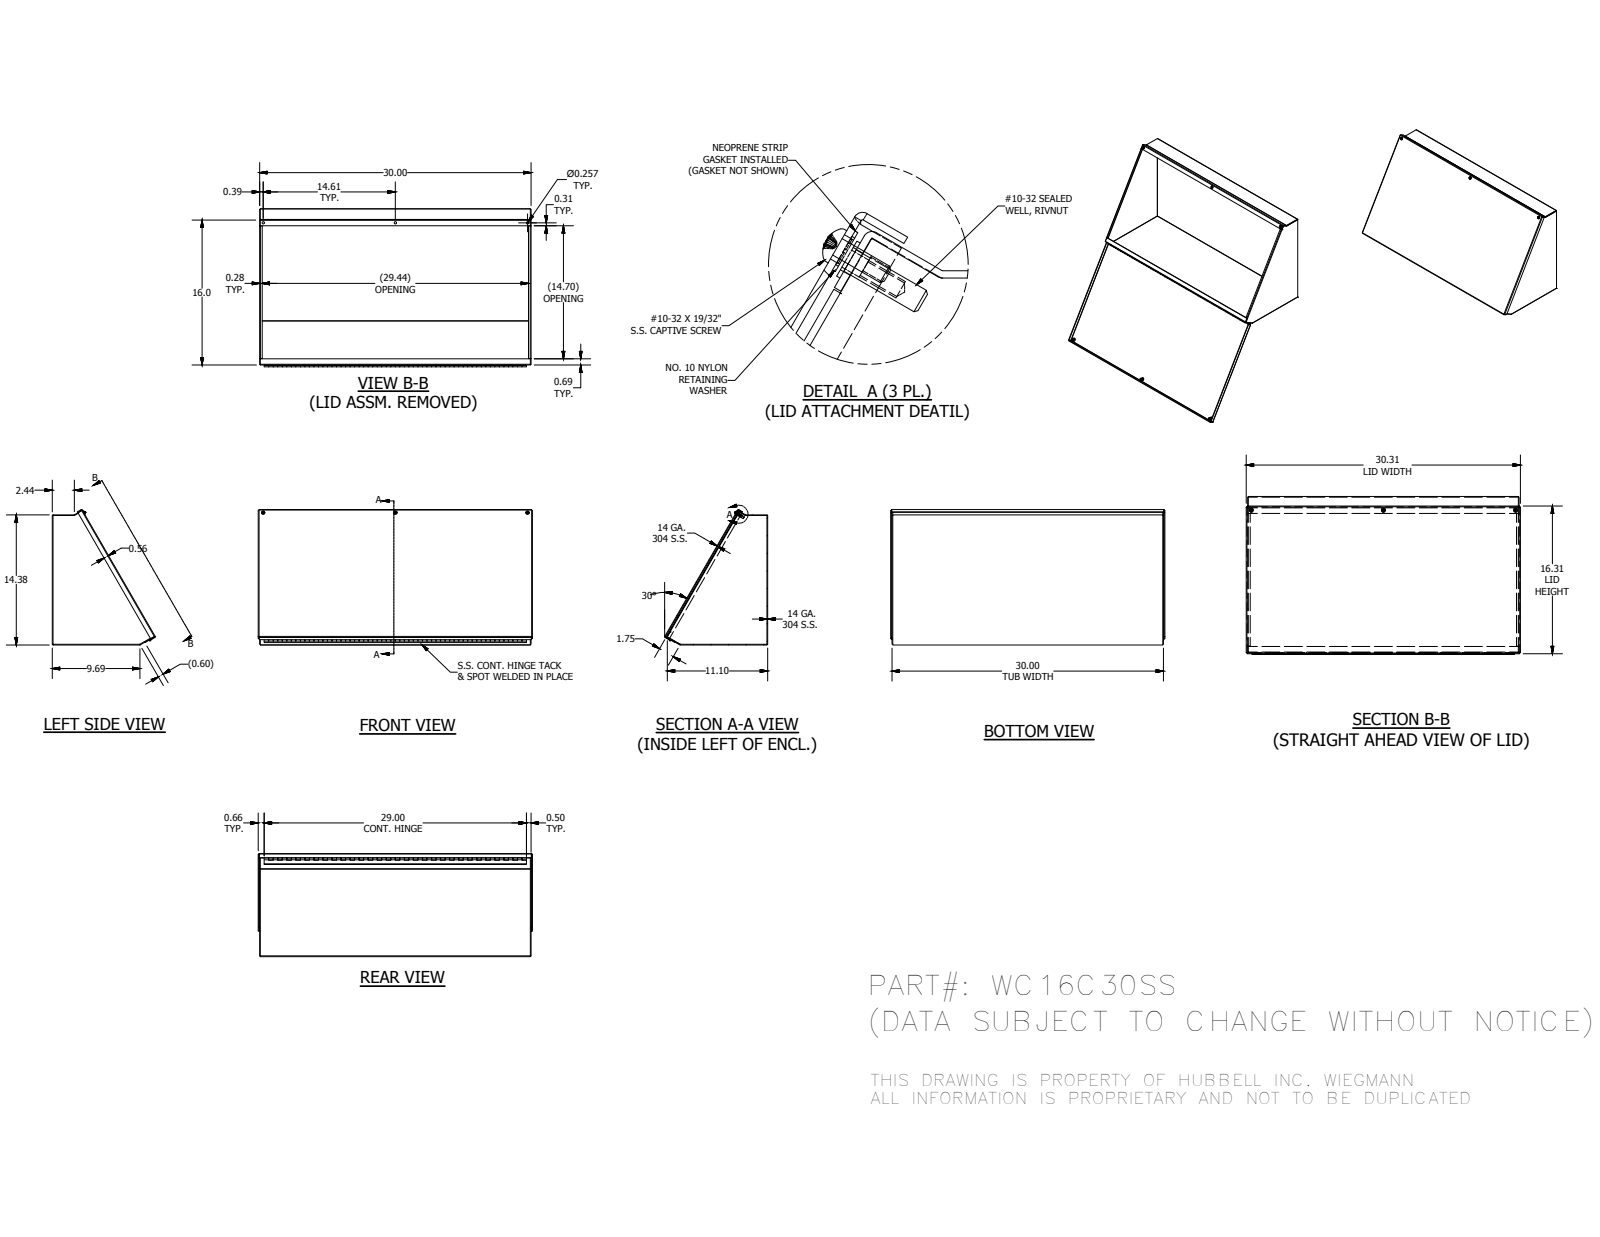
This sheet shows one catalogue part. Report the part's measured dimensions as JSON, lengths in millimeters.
{"part_name": "WC16C30SSBTB; WC16C30SSLID; WC16CSSLS; WC16CSSRS (+8 more)", "step_written_by": "Autodesk Inventor 2014 (AUTOMOTIVE_DESIGN)", "units": "millimeters", "bodies": {"solids": 16, "faces": 657, "planar": 400, "cylindrical": 183, "other": 74}, "overall_size": [769.94, 380, 289.23], "volume_mm3": 2040000, "surface_area_mm2": 2217000, "round_holes": [[3.96, 3], [4.98, 3], [6.53, 3], [7.06, 3], [7.14, 3], [2.96, 1]], "round_bosses_or_shafts": [[11.51, 3], [10.31, 3], [9.47, 3], [6.3, 3], [4.83, 3], [5.08, 1], [2.54, 1]], "partial_cylinders_radius": [[0.4, 12], [2.28, 12], [2.27, 3]], "face_to_face_distances": [1.88, 760.12, 758.24, 762, 363.25, 361.37, 1.87, 365.12, 363.24, 2.94], "hole_center_spacings": [371.17, 742.34, 1.41]}
